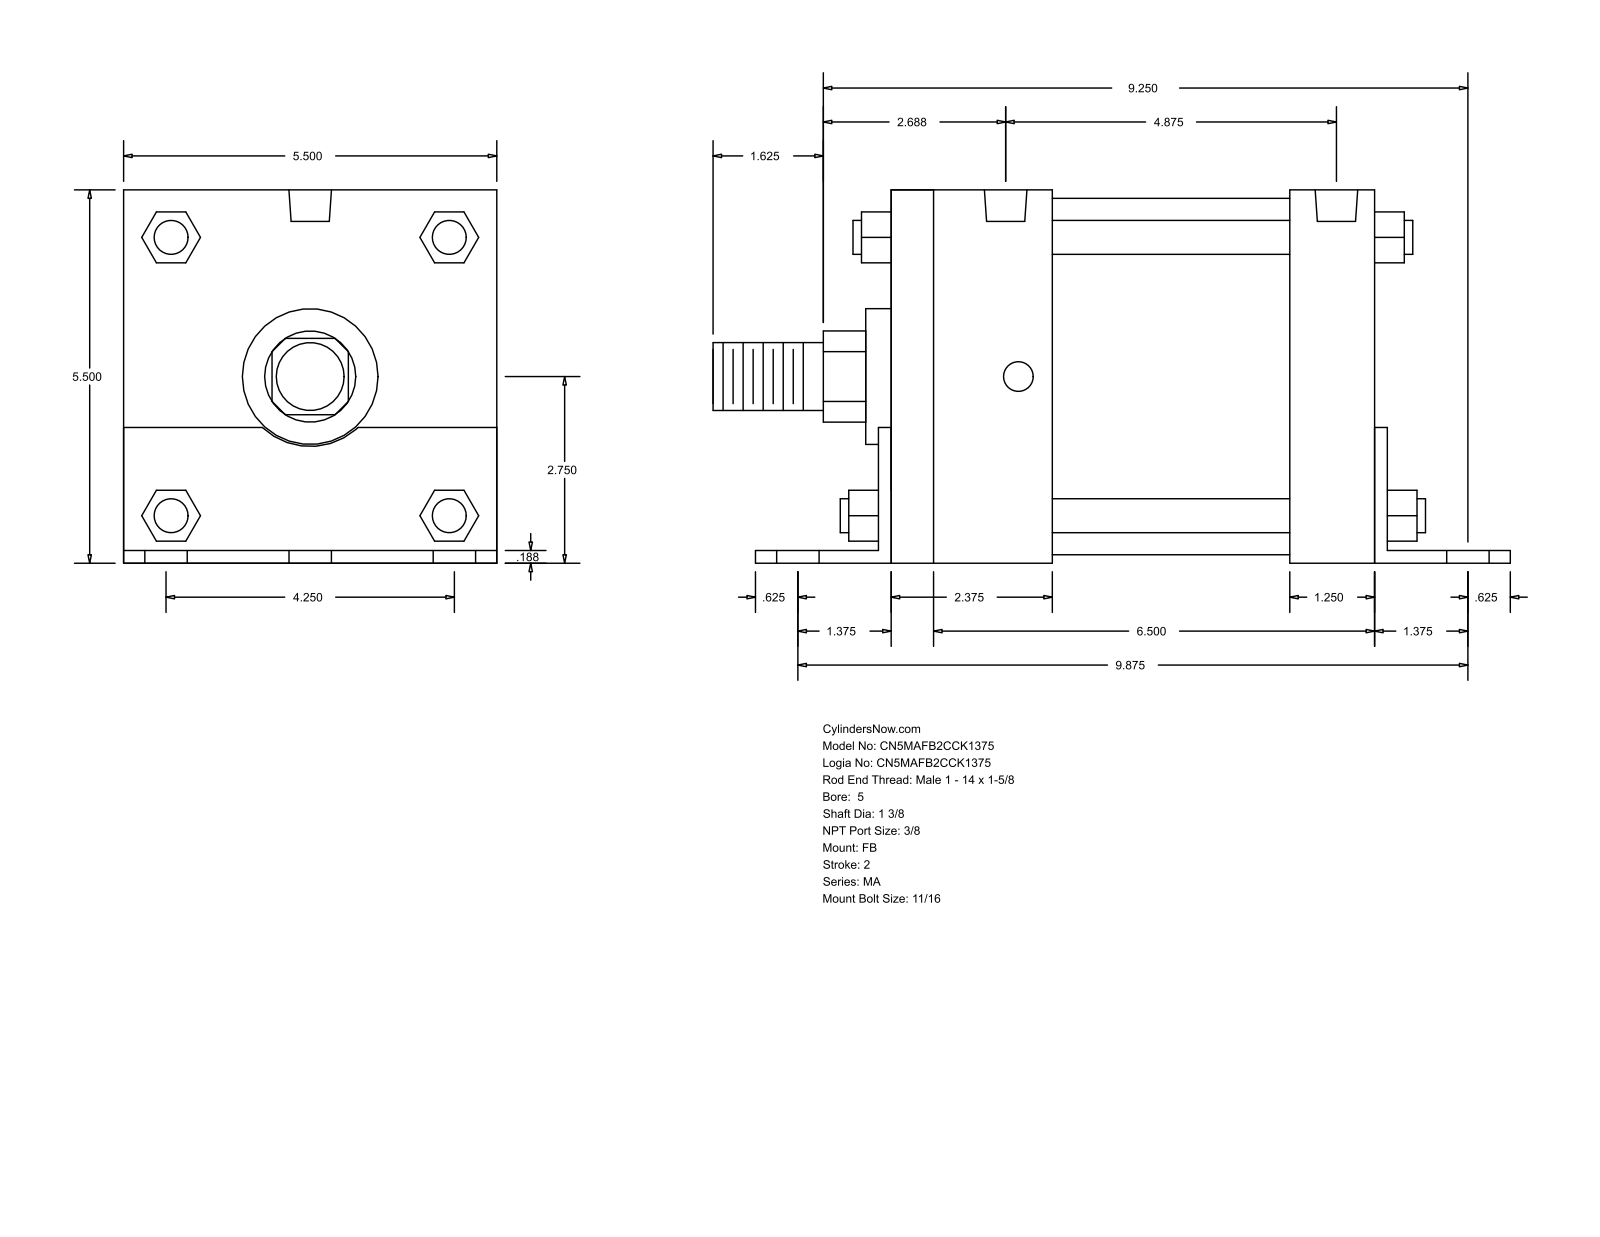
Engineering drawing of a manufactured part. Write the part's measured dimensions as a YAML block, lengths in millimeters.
part_name: "MA_FB__0500_1.375"
step_written_by: "GSSL Pune (CONFIG_CONTROL_DESIGN)"
units: millimeters
bodies: {solids: 0, faces: 140, planar: 105, cylindrical: 35, other: 0}
overall_size: [298.45, 139.75, 139.7]
round_holes:
  - {diameter: 17.46, count: 6}
  - {diameter: 11.11, count: 4}
  - {diameter: 15.93, count: 2}
round_bosses_or_shafts:
  - {diameter: 12.7, count: 4}
  - {diameter: 133.35, count: 1}
  - {diameter: 50.8, count: 1}
  - {diameter: 34.92, count: 1}
  - {diameter: 25.4, count: 1}
partial_cylinders:
  - {radius: 17.06, count: 1}
  - {radius: 26.16, count: 1}
face_to_face_distances: [139.7, 4.76, 139.75, 185.74, 4.71, 134.99, 180.98, 190.5, 36.52, 65.08]
hole_center_spacings: [53.98, 256.57, 250.83, 4.77, 73.04, 76.34, 94.68, 98.64]
